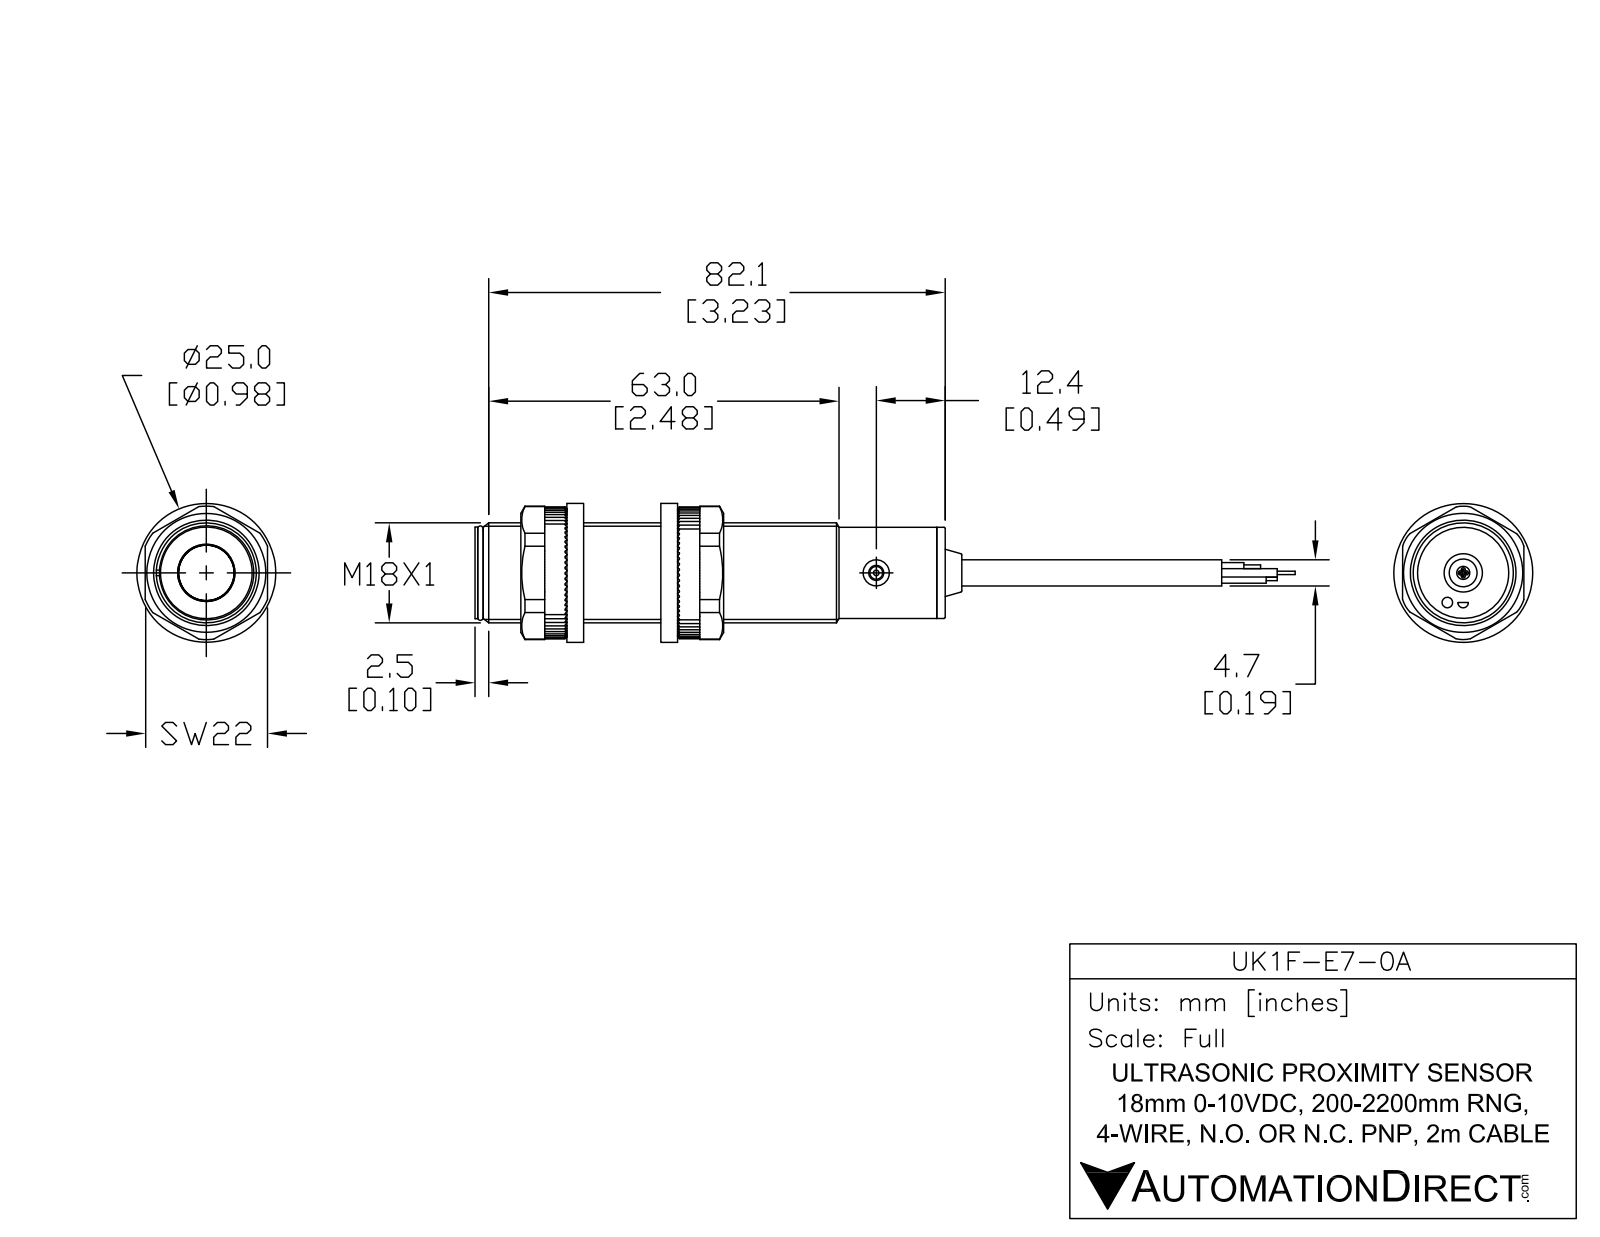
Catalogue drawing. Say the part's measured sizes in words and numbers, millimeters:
The part is named "UK1F-E7-0A". Its 3-D file was written by "SolidWorks 2017 (AUTOMOTIVE_DESIGN)". It is 6 solids with 55 faces: 17 planar, 24 cylindrical and 14 other. Overall it measures 122.7 by 18 by 18 millimeters. Its volume is 21 060 cubic millimeters and its surface area 6 897 square millimeters. Round holes: 2 of diameter 4.7, 1 of diameter 2.7. Round bosses or shafts: 1 of diameter 18, 1 of diameter 16.4, 1 of diameter 15.8, 1 of diameter 9.5, 1 of diameter 4.8, 1 of diameter 2.3. The main face-to-face distances are 81.1, 82.6, 1.5, 1, 82.1, 83.6, 1, 82.1, 83.6, 82.7.
